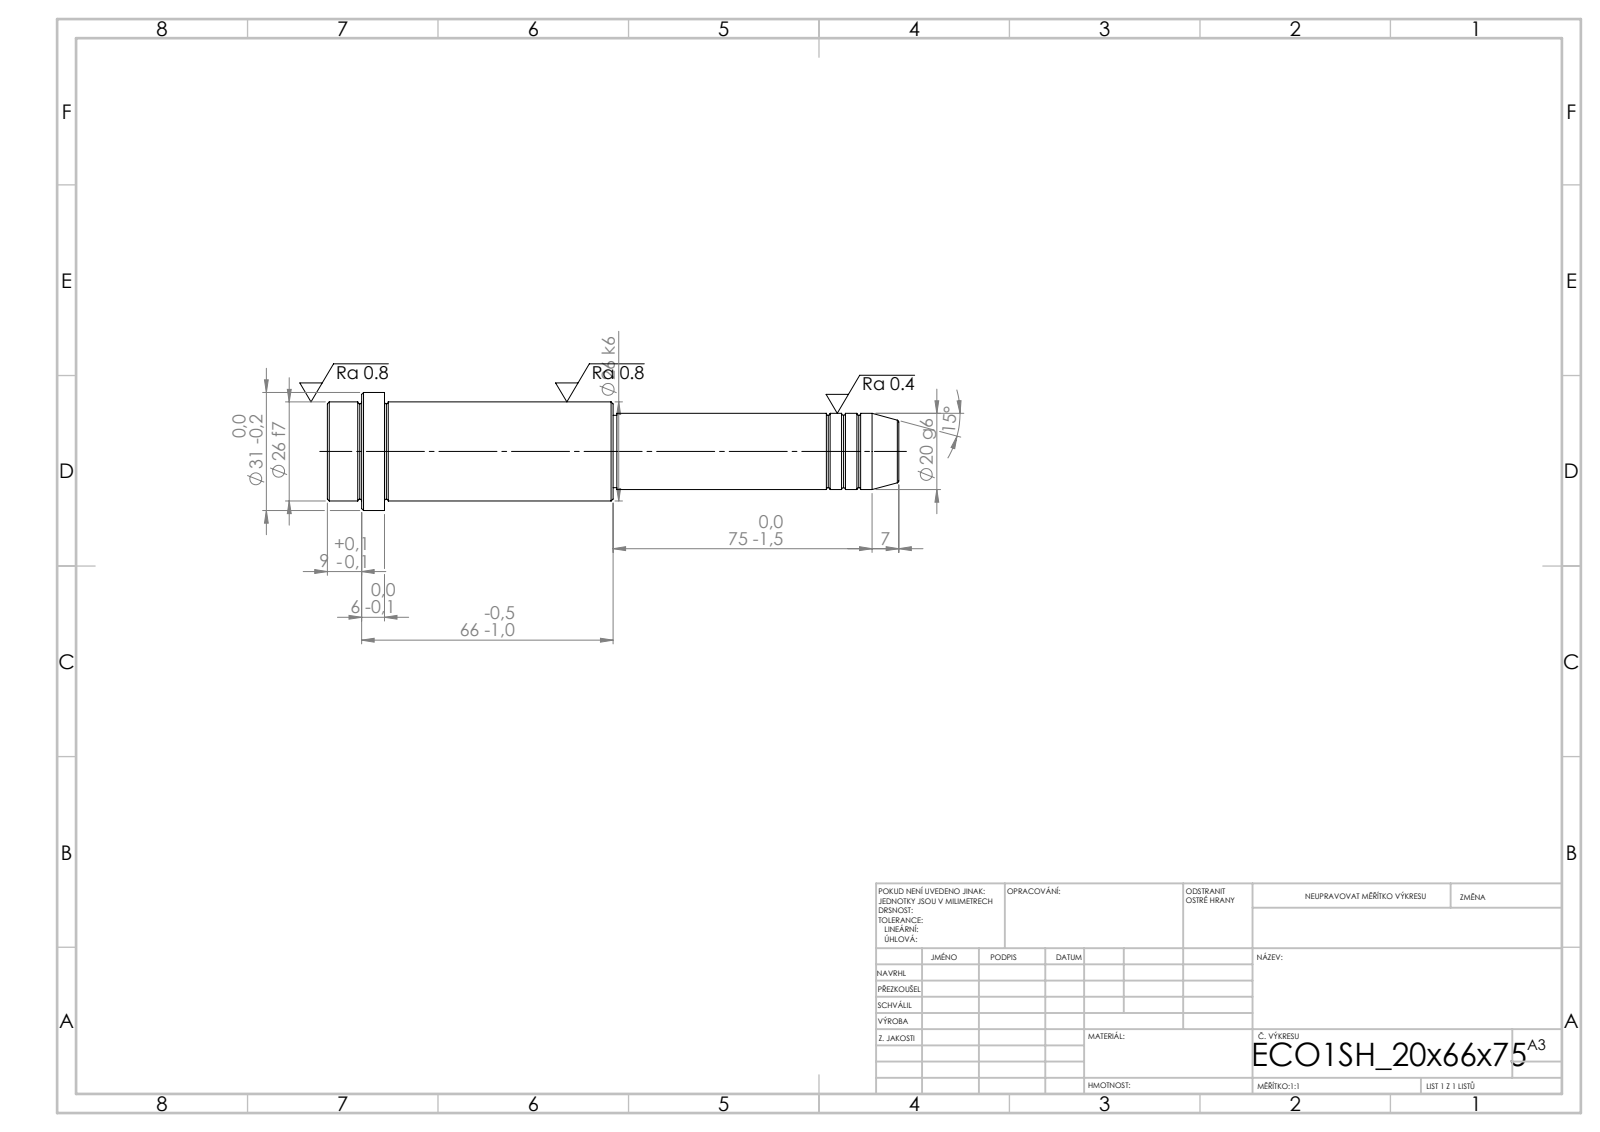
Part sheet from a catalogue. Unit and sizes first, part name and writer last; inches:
Units: inches
Overall size (bounding box): 5.906 × 1.22 × 1.22
Round bosses / shafts (diameter × count): ⌀1.22 ×1, ⌀1.024 ×1, ⌀0.787 ×1, ⌀0.748 ×1
Main face-to-face distances: 2.953, 0.591, 2.362, 5.315, 5.906, 5.551, 2.598, 0.236, 0.354, 2.913
Volume: 3.914 in³ · Surface area: 19.33 in²
Bodies: 1 solid, 52 faces (6 planar, 16 cylindrical, 30 other)
STEP written by: SolidWorks 2019 (CONFIG_CONTROL_DESIGN)
